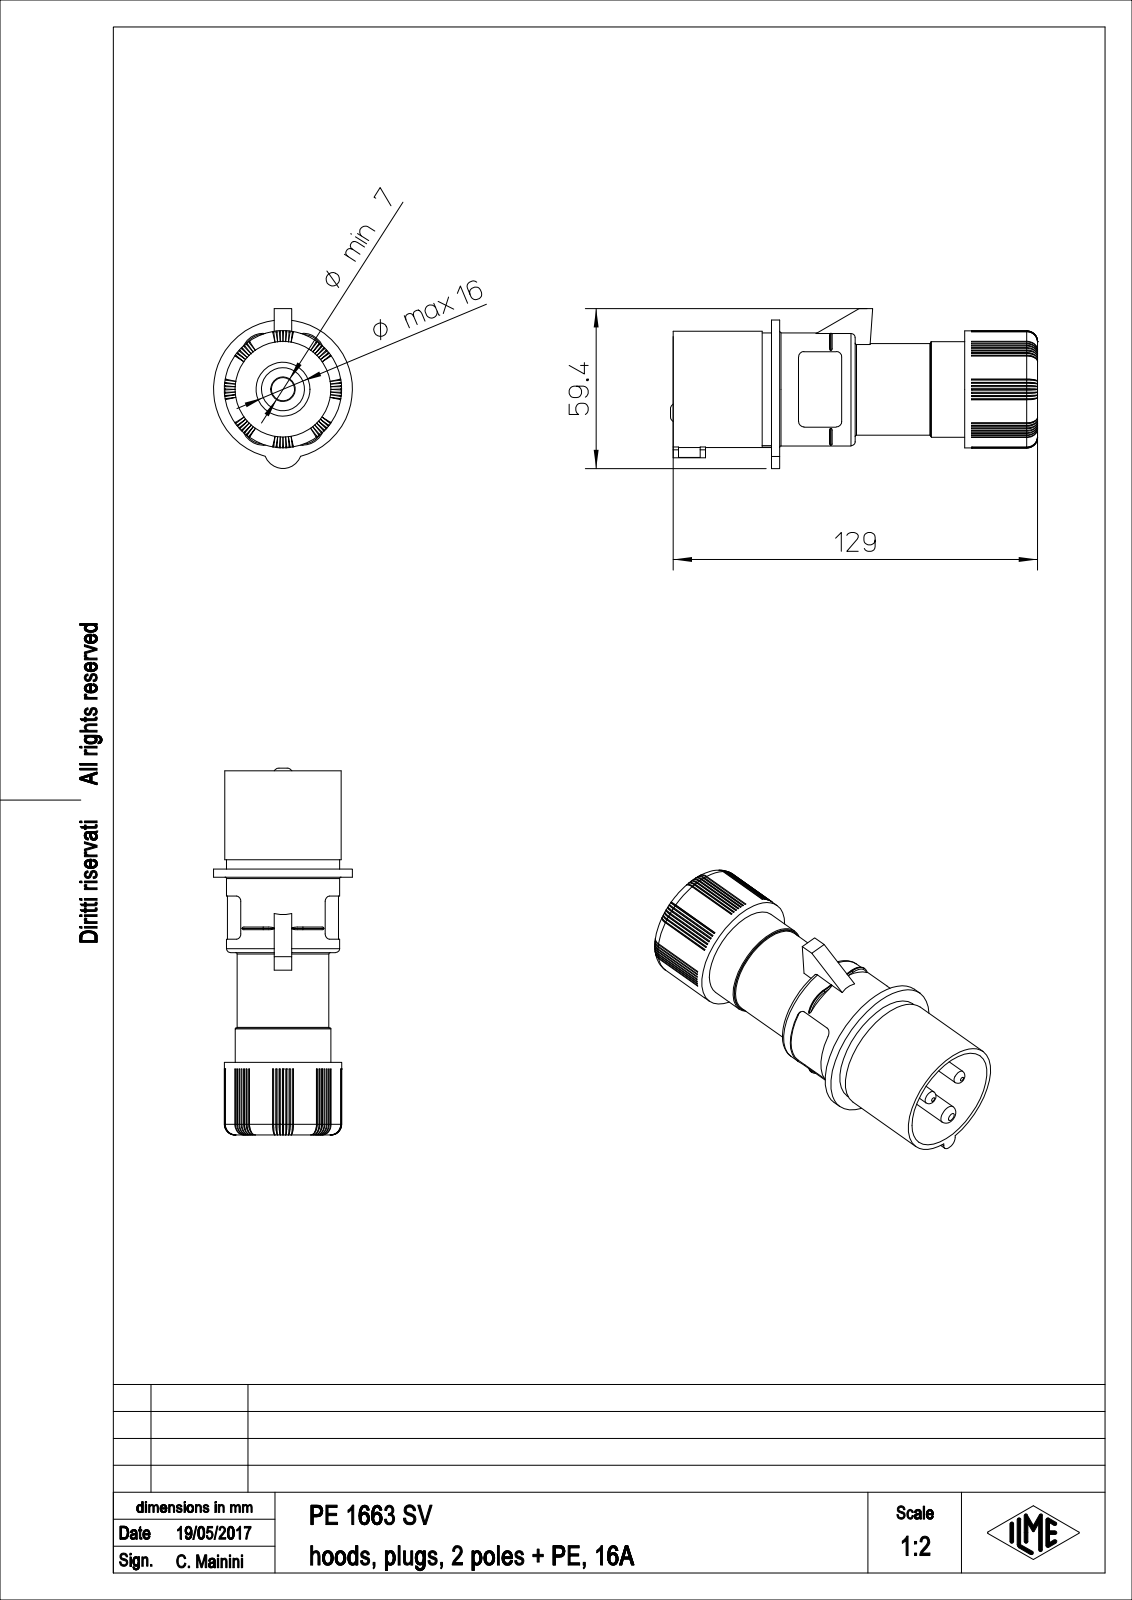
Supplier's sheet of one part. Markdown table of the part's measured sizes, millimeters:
| quantity | value |
| --- | --- |
| part name | PE_1663_SV |
| STEP written by | PTC Creo Elements/Direct Modeling 19.0E 27-Jun-2016 (C) Parametric Technology GmbH (AUTOMOTIVE_DESIGN) |
| units | millimeters |
| bodies | 1 solid, 599 faces (263 planar, 112 cylindrical, 224 other) |
| overall size | 136.2 × 59.4 × 51.5 |
| volume | 115 849 mm³ |
| surface area | 39 830 mm² |
| round holes (diameter × count) | 16 × 1, 20 × 1 |
| round bosses / shafts (diameter × count) | 6.7 × 2, 5 × 2, 51.5 × 1, 43.5 × 1, 43.2 × 1, 42 × 1, 37 × 1, 35.5 × 1 |
| partial cylindrical surfaces (radius × count) | 3.6 × 56, 0.45 × 4, 2 × 4, 8 × 4, 4 × 2, 3 × 1, 7 × 1, 20.6 × 1 |
| main face-to-face distances | 3, 95.7, 98.7, 1.78, 71.7, 68.7, 27, 16, 36.5, 6.5 |
